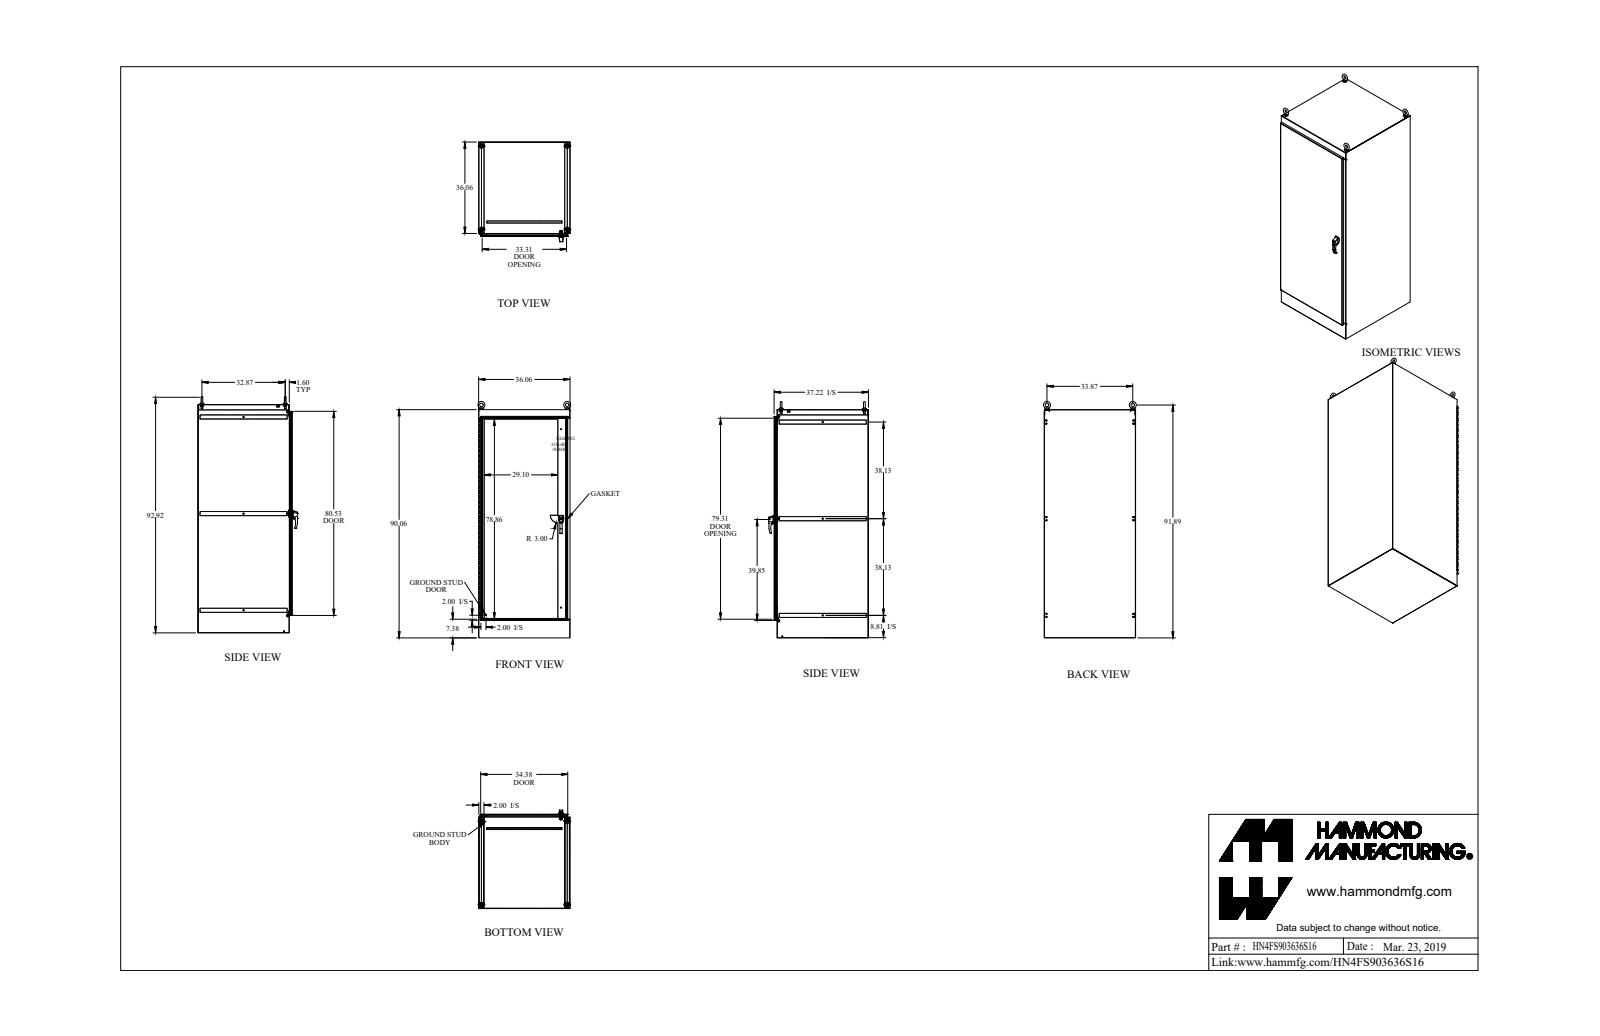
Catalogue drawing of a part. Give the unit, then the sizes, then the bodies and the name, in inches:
Units: inches
Overall size (bounding box): 93.489 × 39.362 × 36.604
Round holes (diameter × count): ⌀0.304 ×13, ⌀0.35 ×7, ⌀0.75 ×6, ⌀0.527 ×4, ⌀0.625 ×4, ⌀0.68 ×4, ⌀0.25 ×3, ⌀0.5 ×3, ⌀0.257 ×2, ⌀0.28 ×2, ⌀0.281 ×2, ⌀0.313 ×2
Round bosses / shafts (diameter × count): ⌀1.75 ×4, ⌀1.5 ×4, ⌀1.25 ×4, ⌀0.738 ×4, ⌀1 ×2, ⌀0.75 ×2, ⌀0.63 ×2, ⌀0.625 ×2
Partial cylindrical surfaces — rounded edges, fillets, slot ends (radius × count): R0.043 ×42, R0.138 ×36, R0.5 ×23, R0.125 ×22, R0.018 ×16, R0.06 ×15, R0.048 ×13, R0.143 ×13
Main face-to-face distances: 0.095, 35.965, 37.152, 35.87, 36.06, 37.057, 37.247, 89.965, 89.87, 90.06
Hole centre spacings: 6, 12, 18, 24, 30, 36, 42, 33.87
Volume: 1 737 in³ · Surface area: 36 498 in²
Bodies: 67 solids, 2394 faces (1040 planar, 996 cylindrical, 358 other)
Part name (STEP PRODUCT): HN4FS903636S16
STEP written by: SolidWorks 2018 (AUTOMOTIVE_DESIGN)
